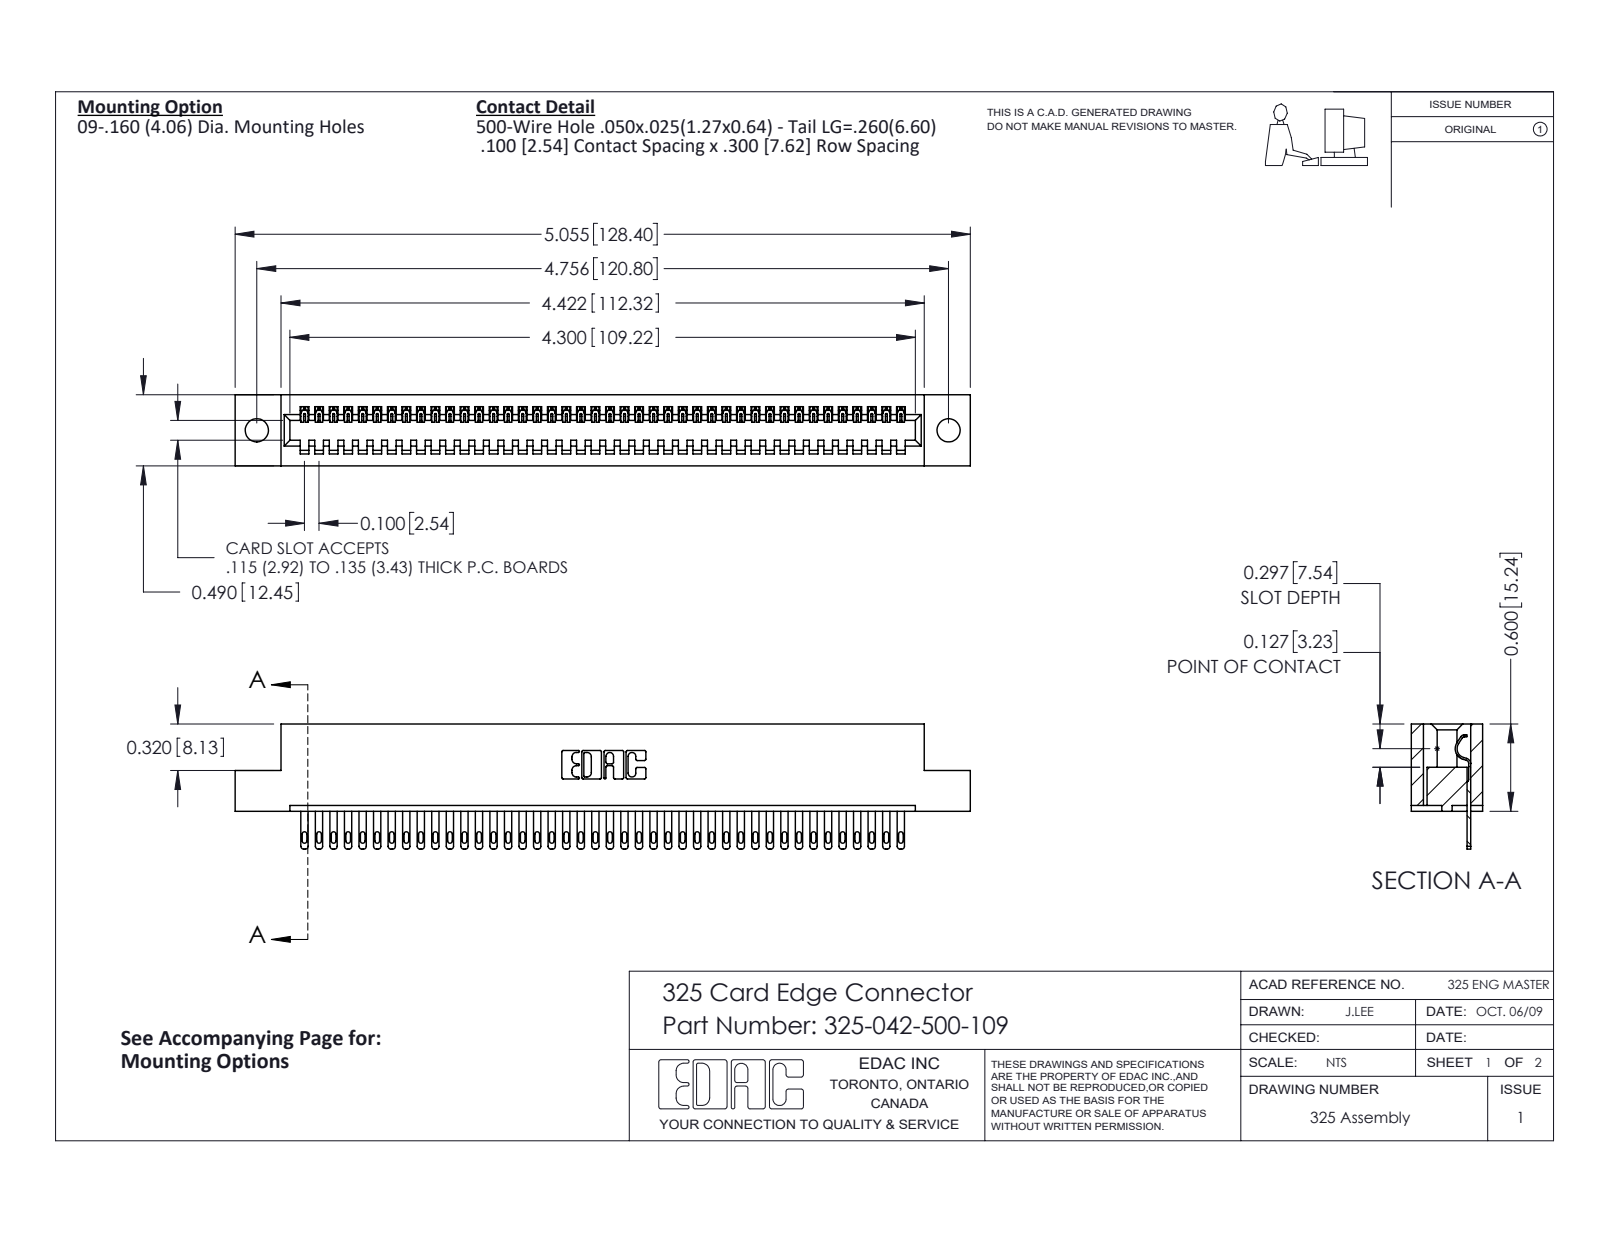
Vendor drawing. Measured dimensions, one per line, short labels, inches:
name: 325 Part_.160 TH; 325-042-500-109; 325-292-001_325-293-100
written by: SolidWorks 2016 (CONFIG_CONTROL_DESIGN)
unit: in
bodies: 43 solids, 2382 faces (1582 planar, 800 cylindrical, 0 other)
size: 5.055 × 0.86 × 0.49
volume: 0.982 in³; area: 27.25 in²
holes: 2× ⌀0.16
rounds: 84× R0.006, 84× R0.016, 84× R0.02, 22× R0.01, 6× R0.007, 6× R0.031, 3× R0.026, 1× R0.014
face distances: 0.083, 0.407, 0.49, 0.3, 0.107, 0.383, 0.025, 0.325, 0.56, 0.04
hole spacings: 4.756
